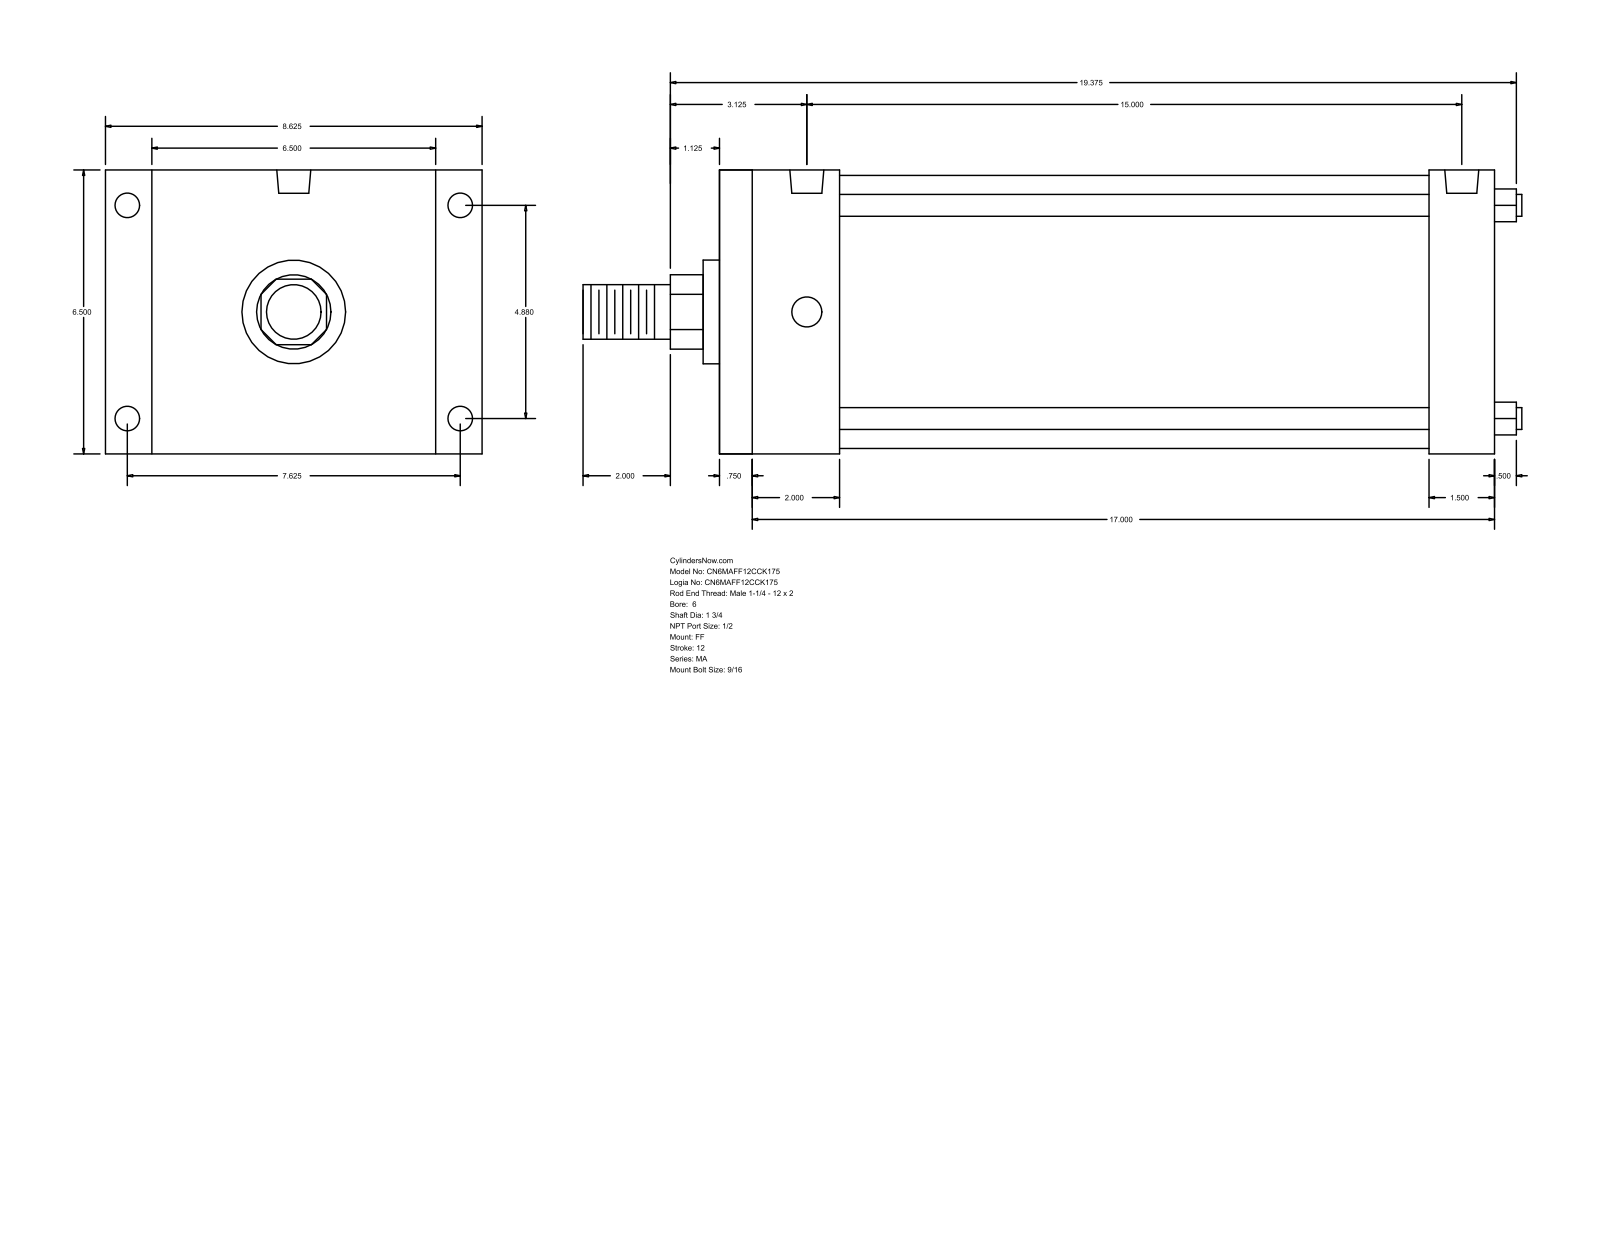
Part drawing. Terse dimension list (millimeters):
name: MA_FF__0600_1.75
written by: GSSL Pune (CONFIG_CONTROL_DESIGN)
unit: mm
bodies: 0 solids, 92 faces (64 planar, 28 cylindrical, 0 other)
size: 546.1 × 219.07 × 165.1
holes: 4× ⌀14.29, 4× ⌀17.46, 2× ⌀19.77
bosses: 4× ⌀12.7, 1× ⌀158.75, 1× ⌀60.33, 1× ⌀44.45, 1× ⌀31.75
rounds: 1× R21.63
face distances: 165.1, 450.86, 19.05, 431.81, 50.8, 69.85, 393.7, 381.01, 412.75, 342.9
hole spacings: 123.96, 193.68, 229.95, 381
